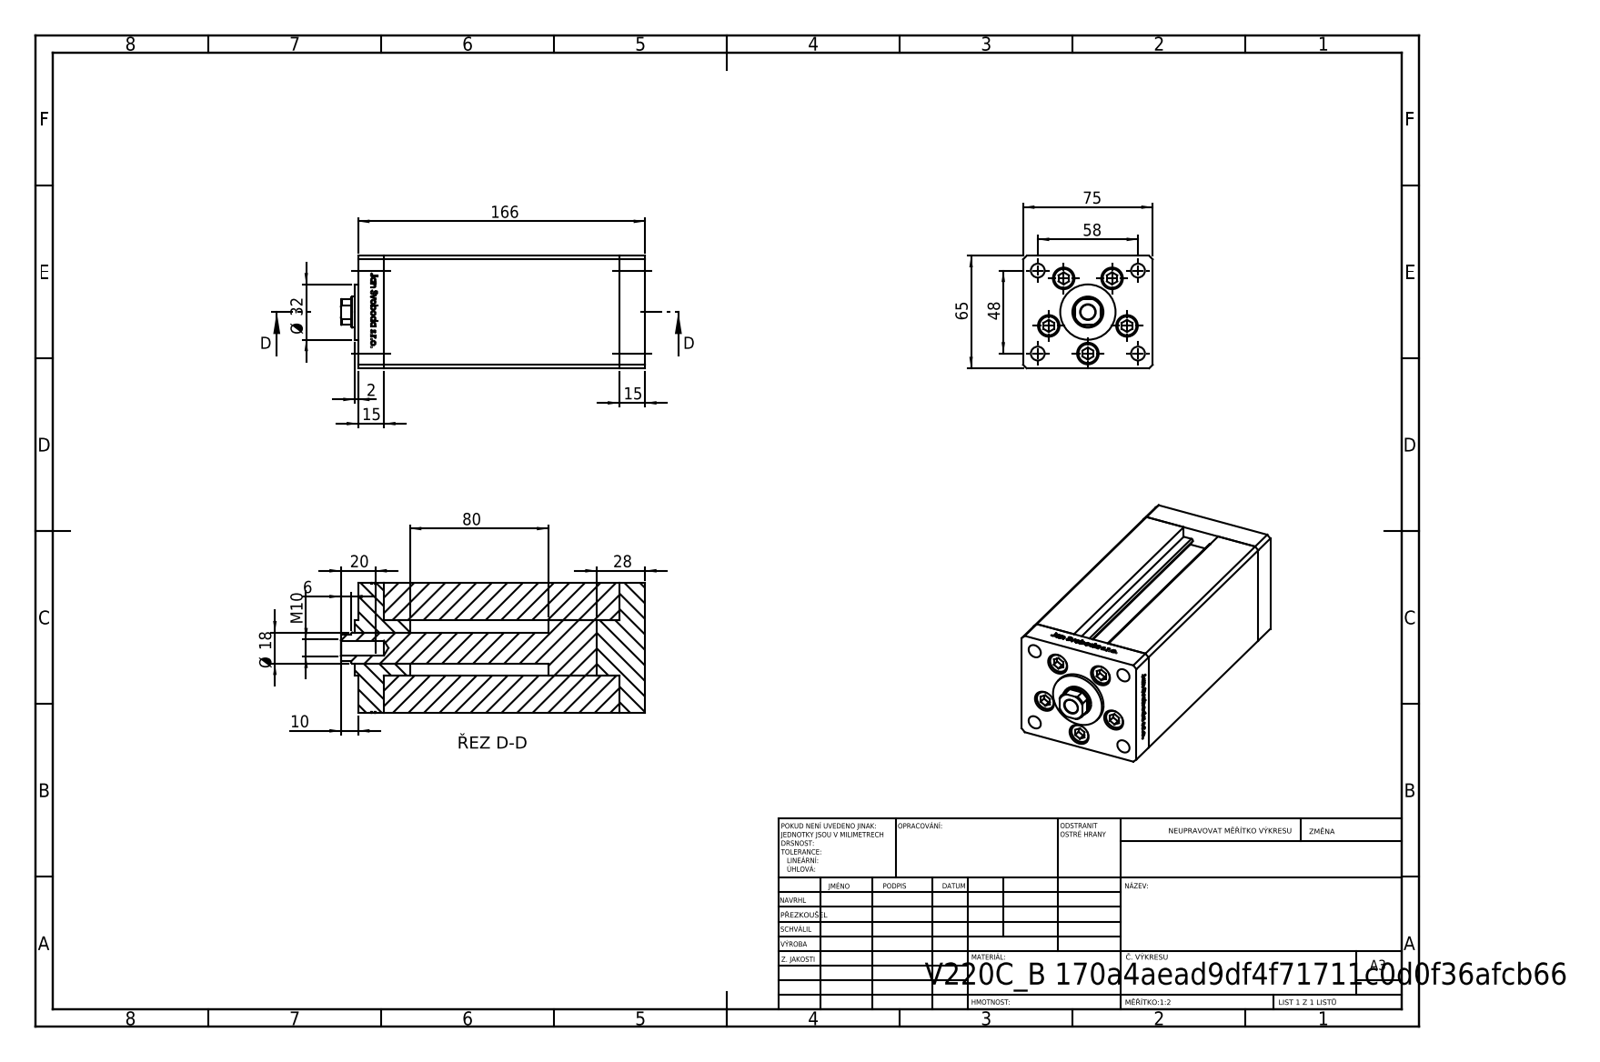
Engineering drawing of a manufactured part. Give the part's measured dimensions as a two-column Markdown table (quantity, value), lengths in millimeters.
| quantity | value |
| --- | --- |
| part name | V220C_FRONT_B; V220C_B MIDDLE; ALLEN BOLT; V220C_VC_B (+1 more) |
| STEP written by | SolidWorks 2019 (CONFIG_CONTROL_DESIGN) |
| units | millimeters |
| bodies | 14 solids, 1183 faces (462 planar, 147 cylindrical, 574 other) |
| overall size | 176 × 75 × 65 |
| volume | 722 498 mm³ |
| surface area | 127 363 mm² |
| round holes (diameter × count) | 9 × 5, 12.5 × 5, 8 × 4, 2 × 2, 13.16 × 2, 8.5 × 1, 18 × 1 |
| round bosses / shafts (diameter × count) | 8 × 5, 32 × 1 |
| partial cylindrical surfaces (radius × count) | 0.93 × 2, 8.5 × 1 |
| main face-to-face distances | 75, 65, 15, 136, 151, 166, 28, 13, 54.5, 10.5 |
| hole center spacings | 24, 37.64, 15.67, 17.22, 27.71, 28.83, 29, 32.63 |
